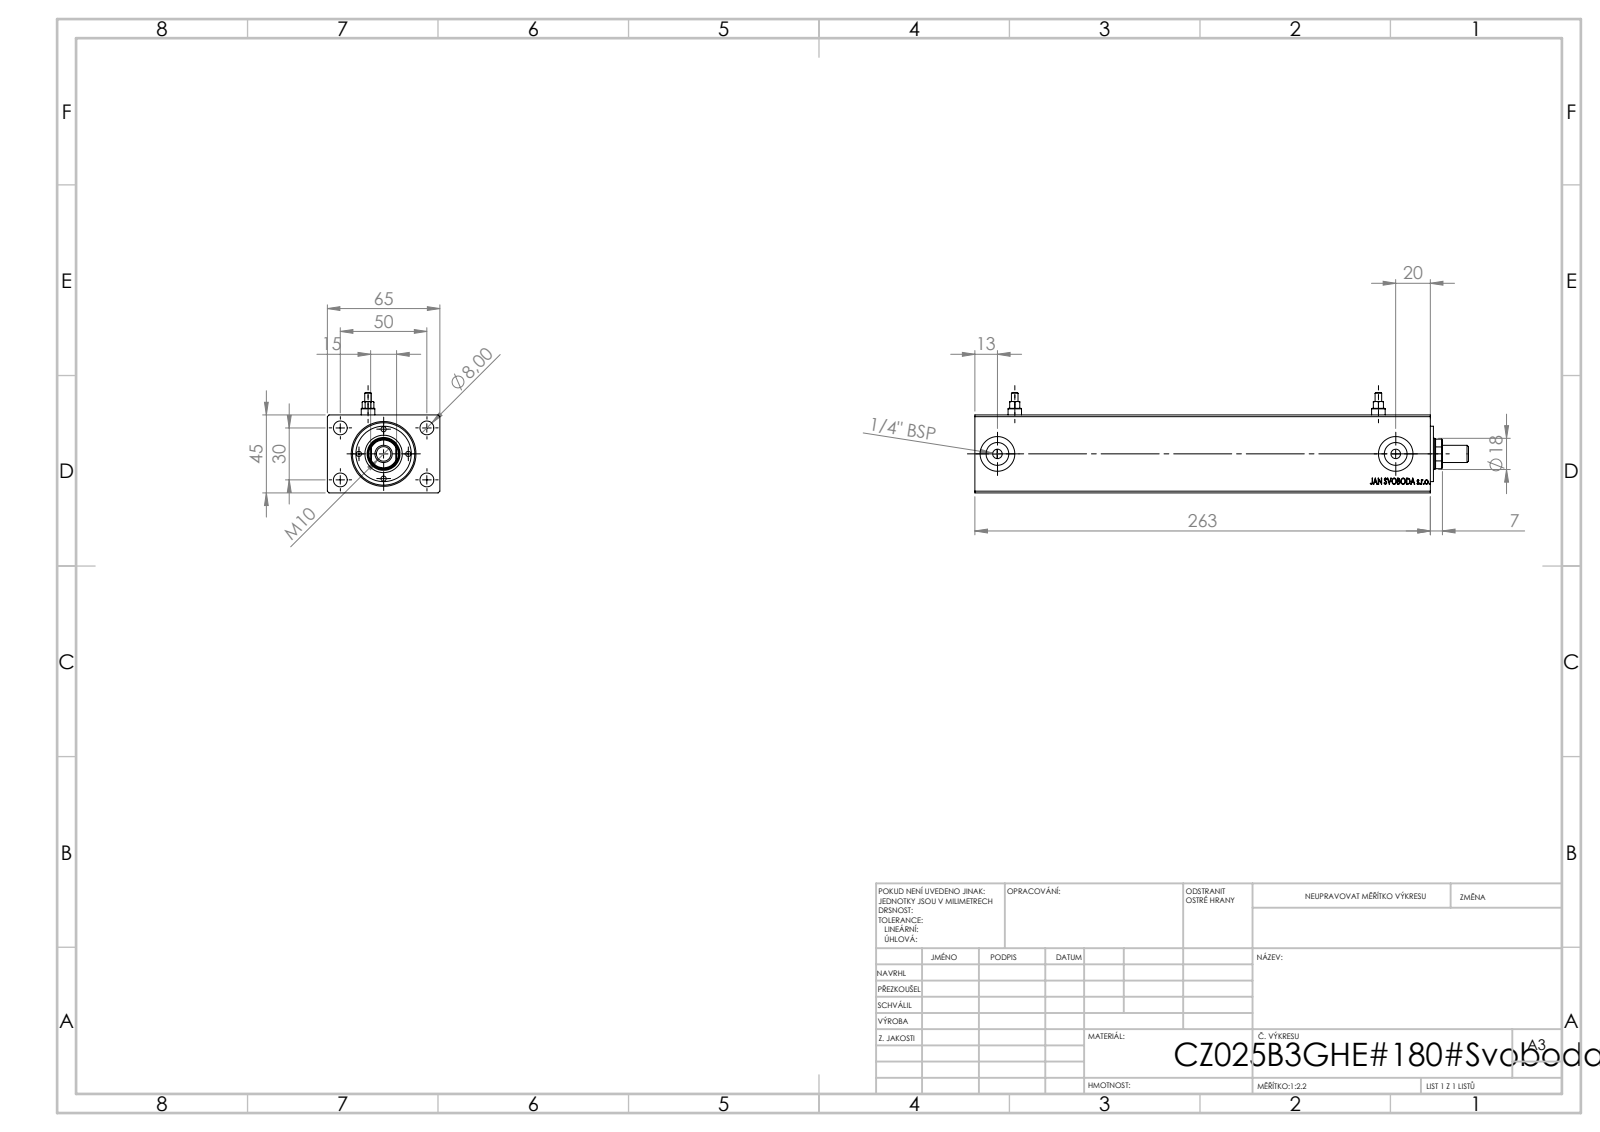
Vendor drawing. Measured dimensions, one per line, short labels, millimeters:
name: V500CZ_B_VC; Zatka_Cushioning3; V500CZ; V500CZ_SMALL_MALE_METRIC
written by: SolidWorks 2019 (CONFIG_CONTROL_DESIGN)
unit: mm
bodies: 6 solids, 939 faces (425 planar, 76 cylindrical, 438 other)
size: 285 × 65 × 58
volume: 713 767 mm³; area: 110 728 mm²
holes: 6× ⌀8, 4× ⌀3, 2× ⌀1.8, 2× ⌀5.5, 2× ⌀13.16, 2× ⌀20, 1× ⌀8.5, 1× ⌀18, 1× ⌀19, 1× ⌀25, 1× ⌀36
bosses: 2× ⌀7.8, 2× ⌀3.8, 1× ⌀32, 1× ⌀10
rounds: 1× R8.5
face distances: 45, 65, 263, 7, 262.8, 5.2, 12.8, 250.2, 12.6, 1.8
hole spacings: 14.25, 18.45, 20.15, 25.01, 29.15, 38.48, 42.02, 28.5
